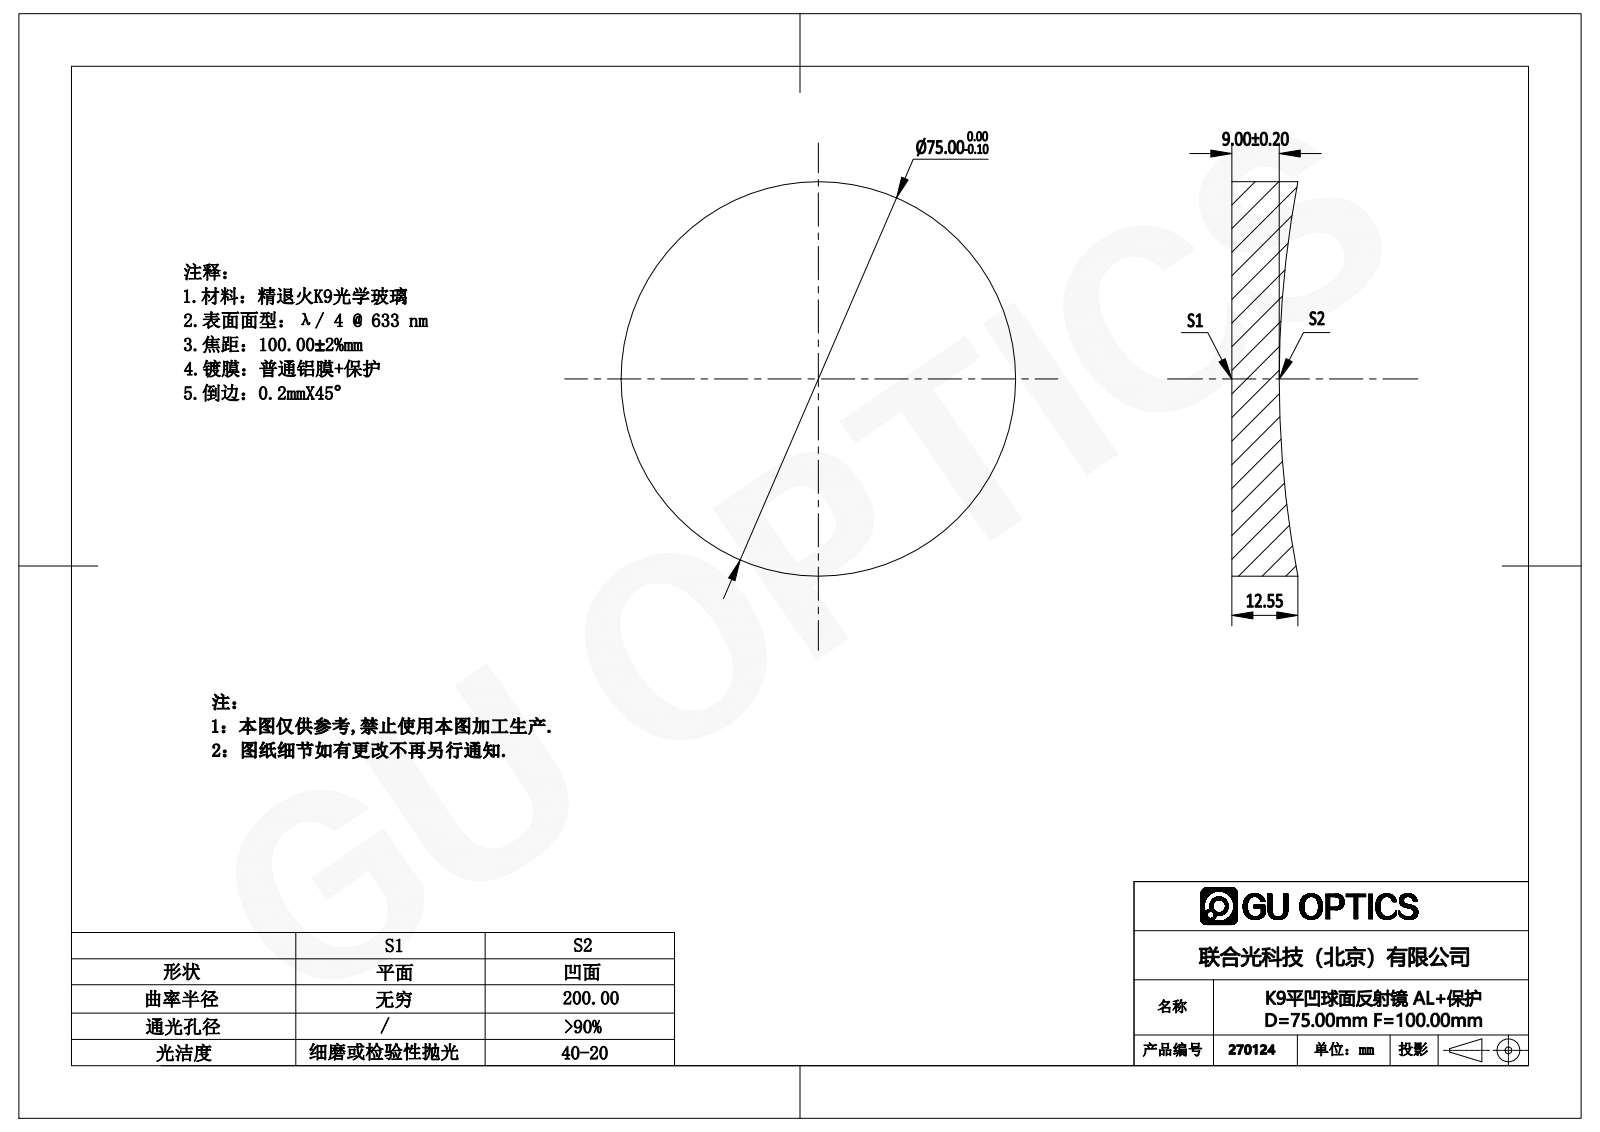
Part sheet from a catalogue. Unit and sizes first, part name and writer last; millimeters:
Units: millimetres
Overall size (bounding box): 75 × 75 × 12.55
Round bosses / shafts (diameter × count): ⌀75 ×1
Volume: 47 573 mm³ · Surface area: 11 832 mm²
Bodies: 1 solid, 5 faces (1 planar, 2 cylindrical, 2 other)
Part name (STEP PRODUCT): 270059
STEP written by: SolidWorks 2016 (AUTOMOTIVE_DESIGN)
